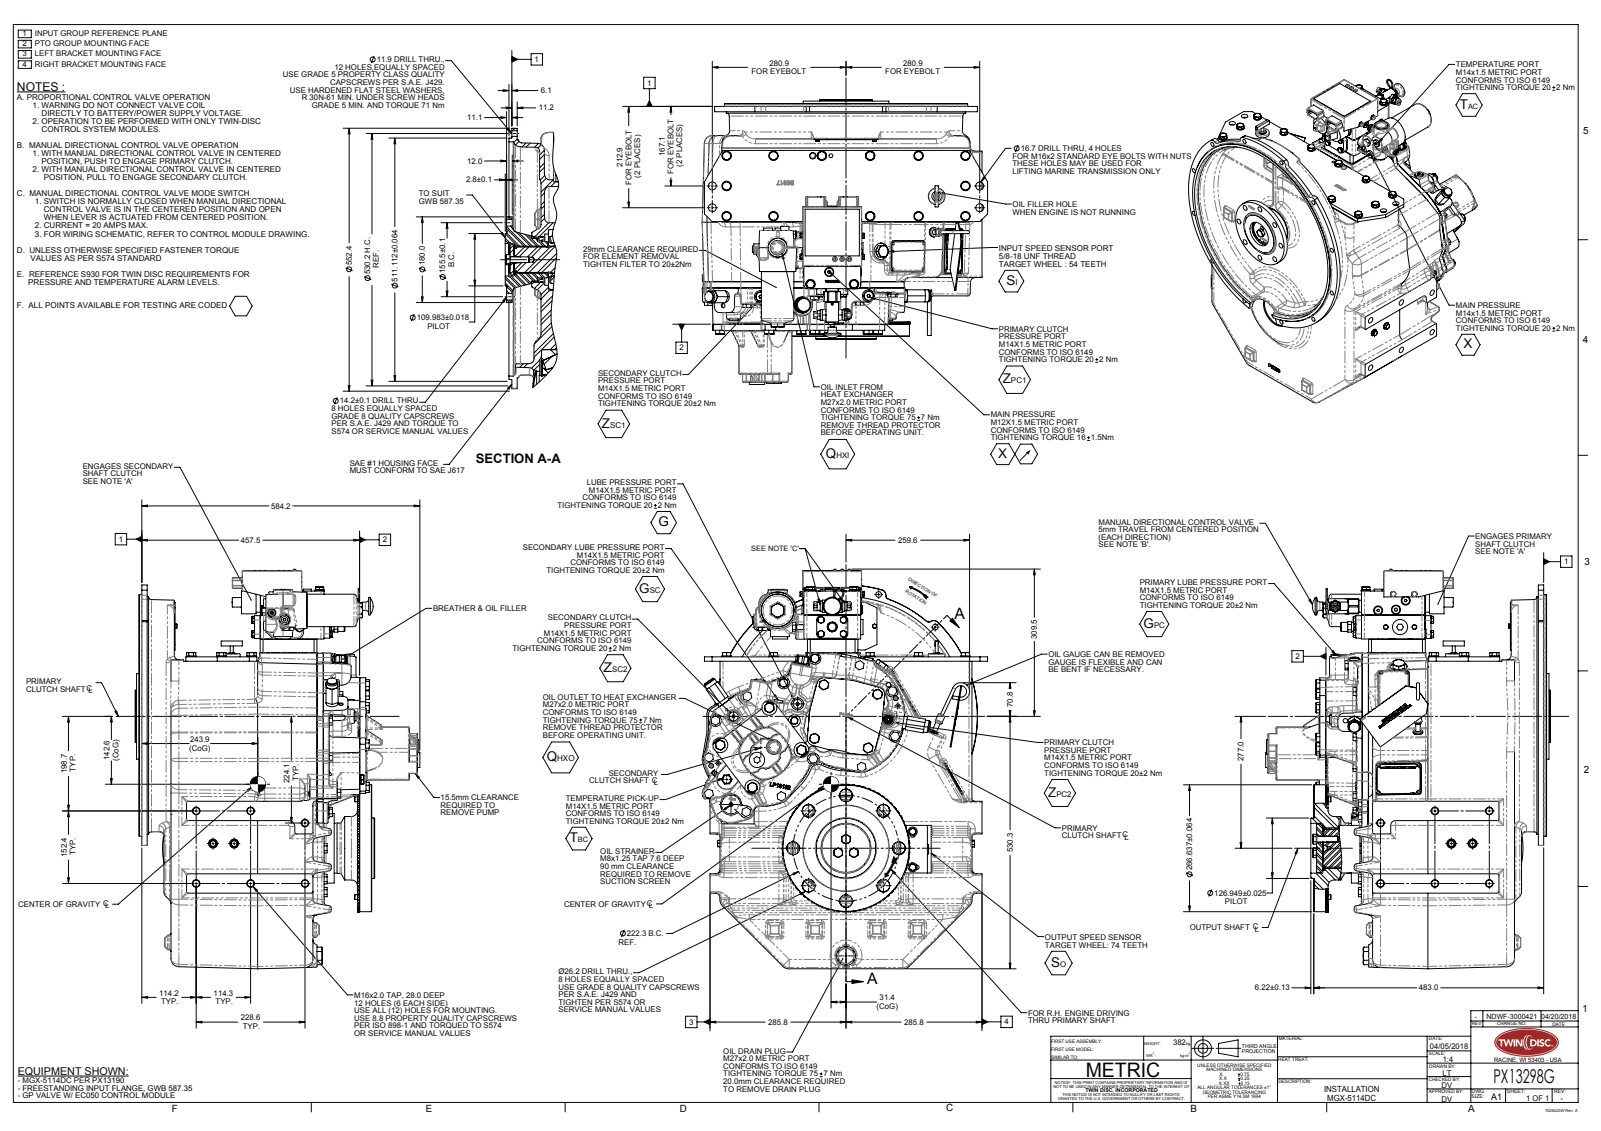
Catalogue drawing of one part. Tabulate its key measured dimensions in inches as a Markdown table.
| quantity | value |
| --- | --- |
| part name | PX13298G |
| STEP written by | SolidWorks 2015 (AUTOMOTIVE_DESIGN) |
| units | inches |
| bodies | 0 solids, 3829 faces (1453 planar, 1129 cylindrical, 1247 other) |
| overall size | 33.06 × 23.606 × 23.547 |
| round holes (diameter × count) | 0.469 × 12, 0.559 × 8, 1.031 × 8, 0.44 × 7, 0.63 × 6, 0.656 × 4, 0.748 × 4, 0.984 × 4, 0.102 × 3, 0.375 × 3, 0.394 × 3, 0.173 × 2 |
| round bosses / shafts (diameter × count) | 0.781 × 16, 0.744 × 9, 0.1 × 5, 0.787 × 4, 0.492 × 4, 0.75 × 3, 0.25 × 3, 1.9 × 2 |
| partial cylindrical surfaces (radius × count) | 1.808 × 101, 0.059 × 86, 0.079 × 68, 0.197 × 66, 0.394 × 65, 0.315 × 49, 0.118 × 28, 0.669 × 26 |
| main face-to-face distances | 12.607, 0.017, 12.591, 0.365, 0.851, 0.867, 11.74, 0.533, 0.516, 0.335 |
| hole center spacings | 10.437, 5.403, 10.437, 14.761, 18.078, 20.163, 4.375, 5.402 |
